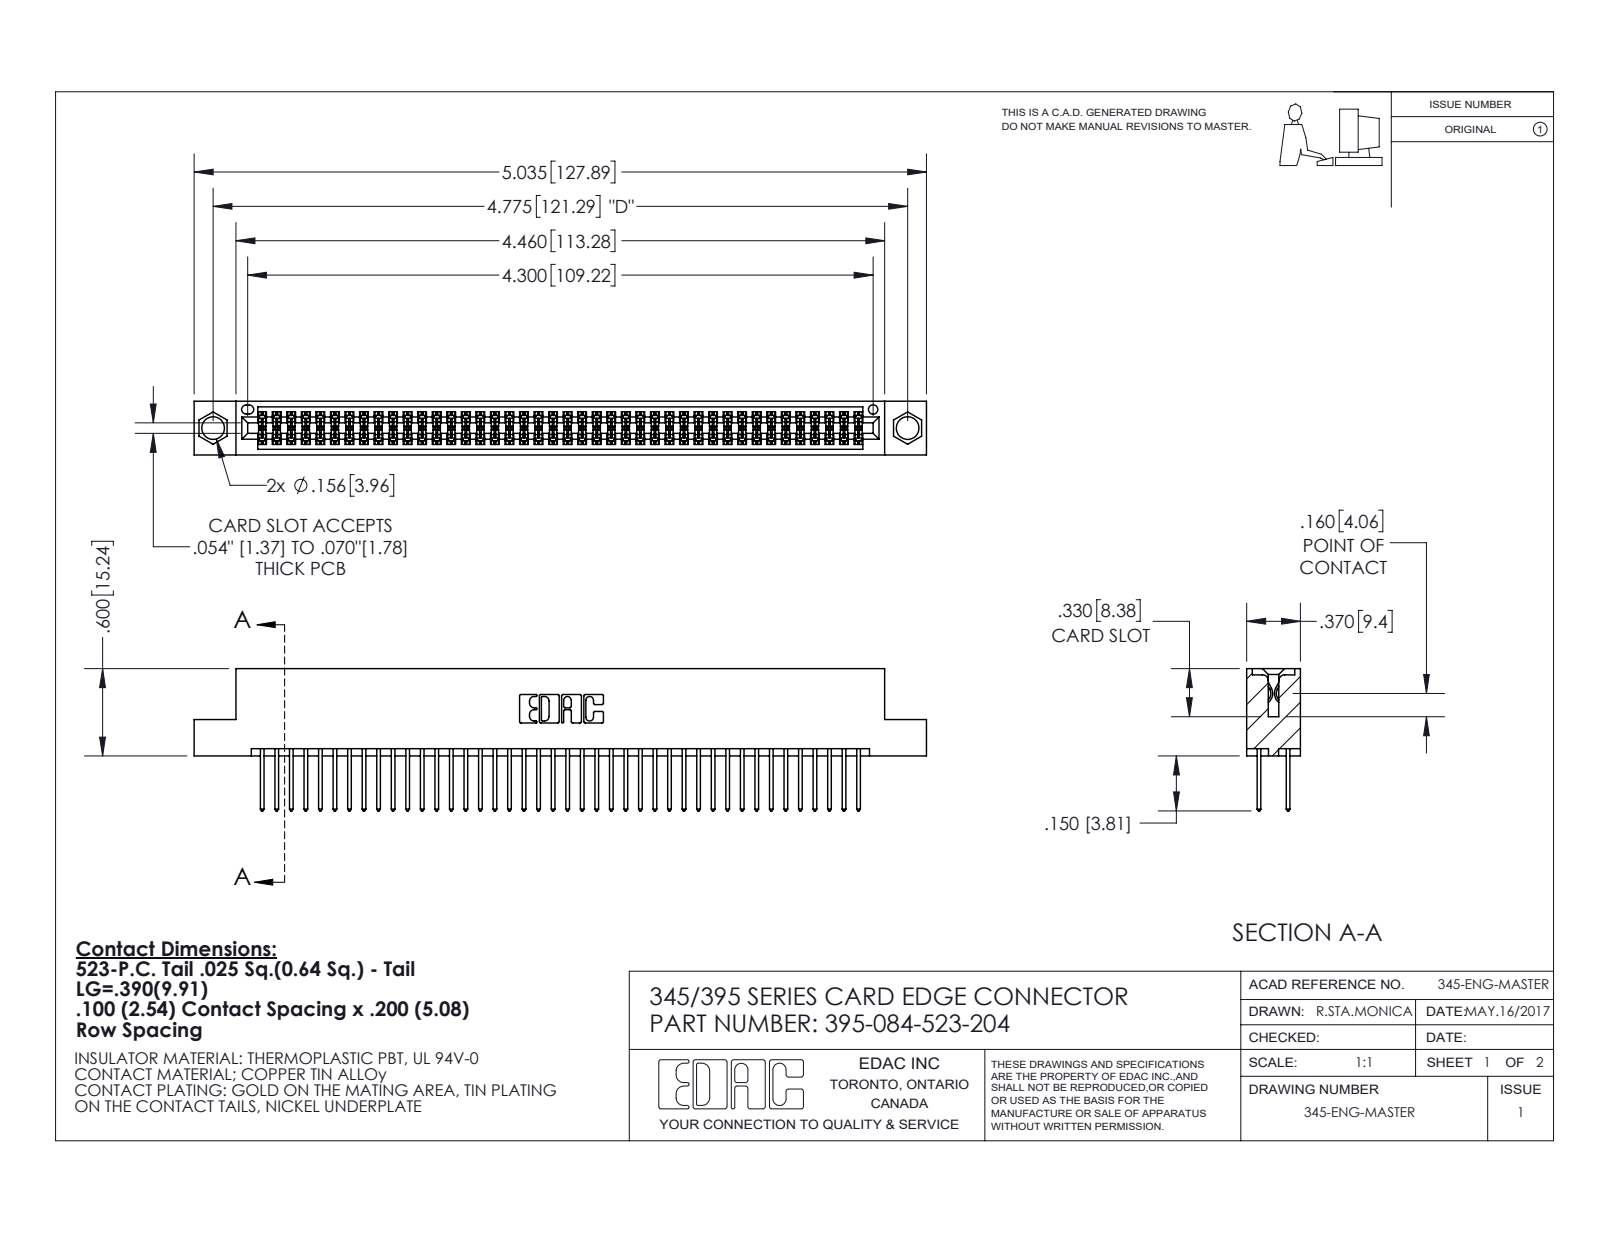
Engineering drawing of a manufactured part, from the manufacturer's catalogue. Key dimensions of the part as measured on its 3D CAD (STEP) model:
Part name (STEP PRODUCT): 345-292-001_345-293-123; 395-084-523-204; 345 Part_Flush Mounting Lugs - 0.156 Dia-TI
STEP written by: SolidWorks 2020 (CONFIG_CONTROL_DESIGN)
Units: inches
Bodies: 85 solids, 4340 faces (2866 planar, 1474 cylindrical, 0 other)
Overall size (bounding box): 5.035 × 0.977 × 0.37
Volume: 0.762 in³ · Surface area: 29.58 in²
Round holes (diameter × count): ⌀0.156 ×2, ⌀0.064 ×1
Partial cylindrical surfaces — rounded edges, fillets, slot ends (radius × count): R0.006 ×168, R0.01 ×84, R0.01 ×22, R0.007 ×6, R0.031 ×6, R0.026 ×3, R0.014 ×2, R0.019 ×2
Main face-to-face distances: 0.072, 0.298, 0.2, 0.098, 0.272, 0.025, 0.37, 0.225, 0.175, 0.149
Hole centre spacings: 0.27, 4.539, 4.775
